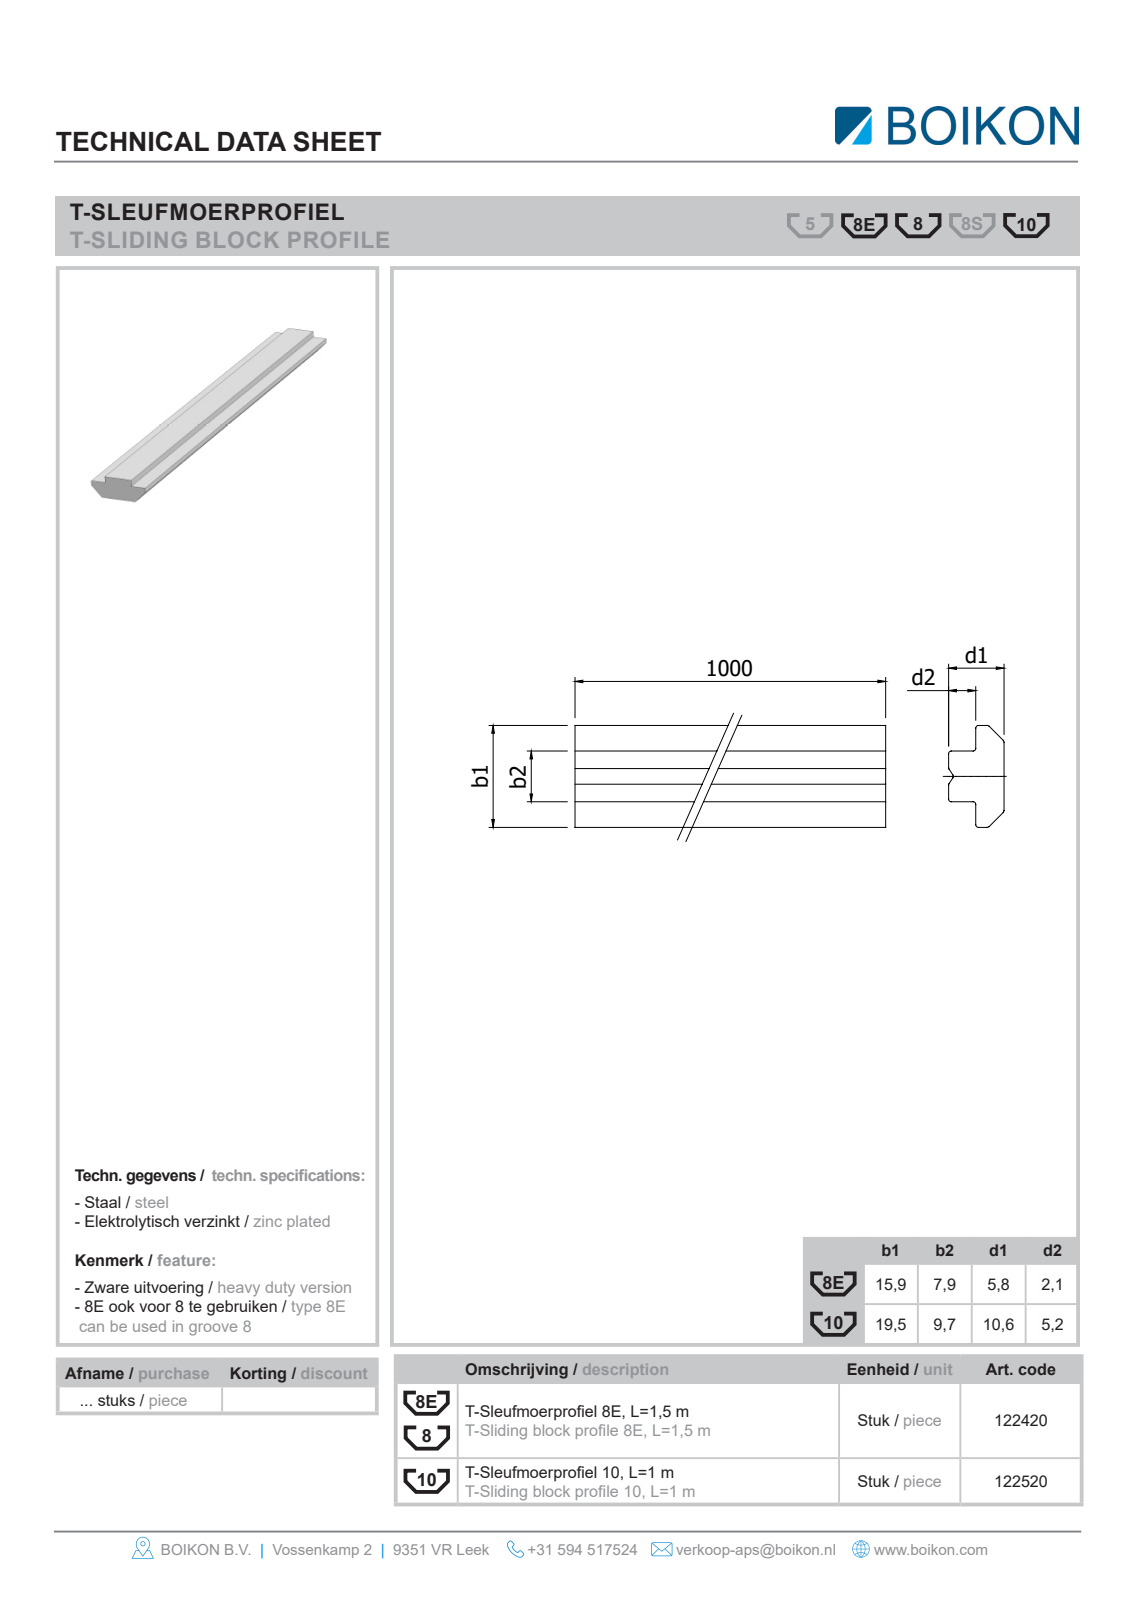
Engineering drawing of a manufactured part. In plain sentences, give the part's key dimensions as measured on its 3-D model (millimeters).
The part is named "Root; 122520T-Sleufmoerprofiel 10 L=1mBOIKON0". Its 3-D file was written by "HiCAD 2013 1802.4 Build 509 (AUTOMOTIVE_DESIGN)". It is 1 solid with 12 faces: 12 planar, 0 cylindrical and 0 other. Overall it measures 1000 by 19.5 by 10.5 millimeters. Its volume is 156 550 cubic millimeters and its surface area 56 798 square millimeters. The main face-to-face distances are 6.5, 10.5, 4, 4.9, 14.6, 9.7, 19.5, 1000.
